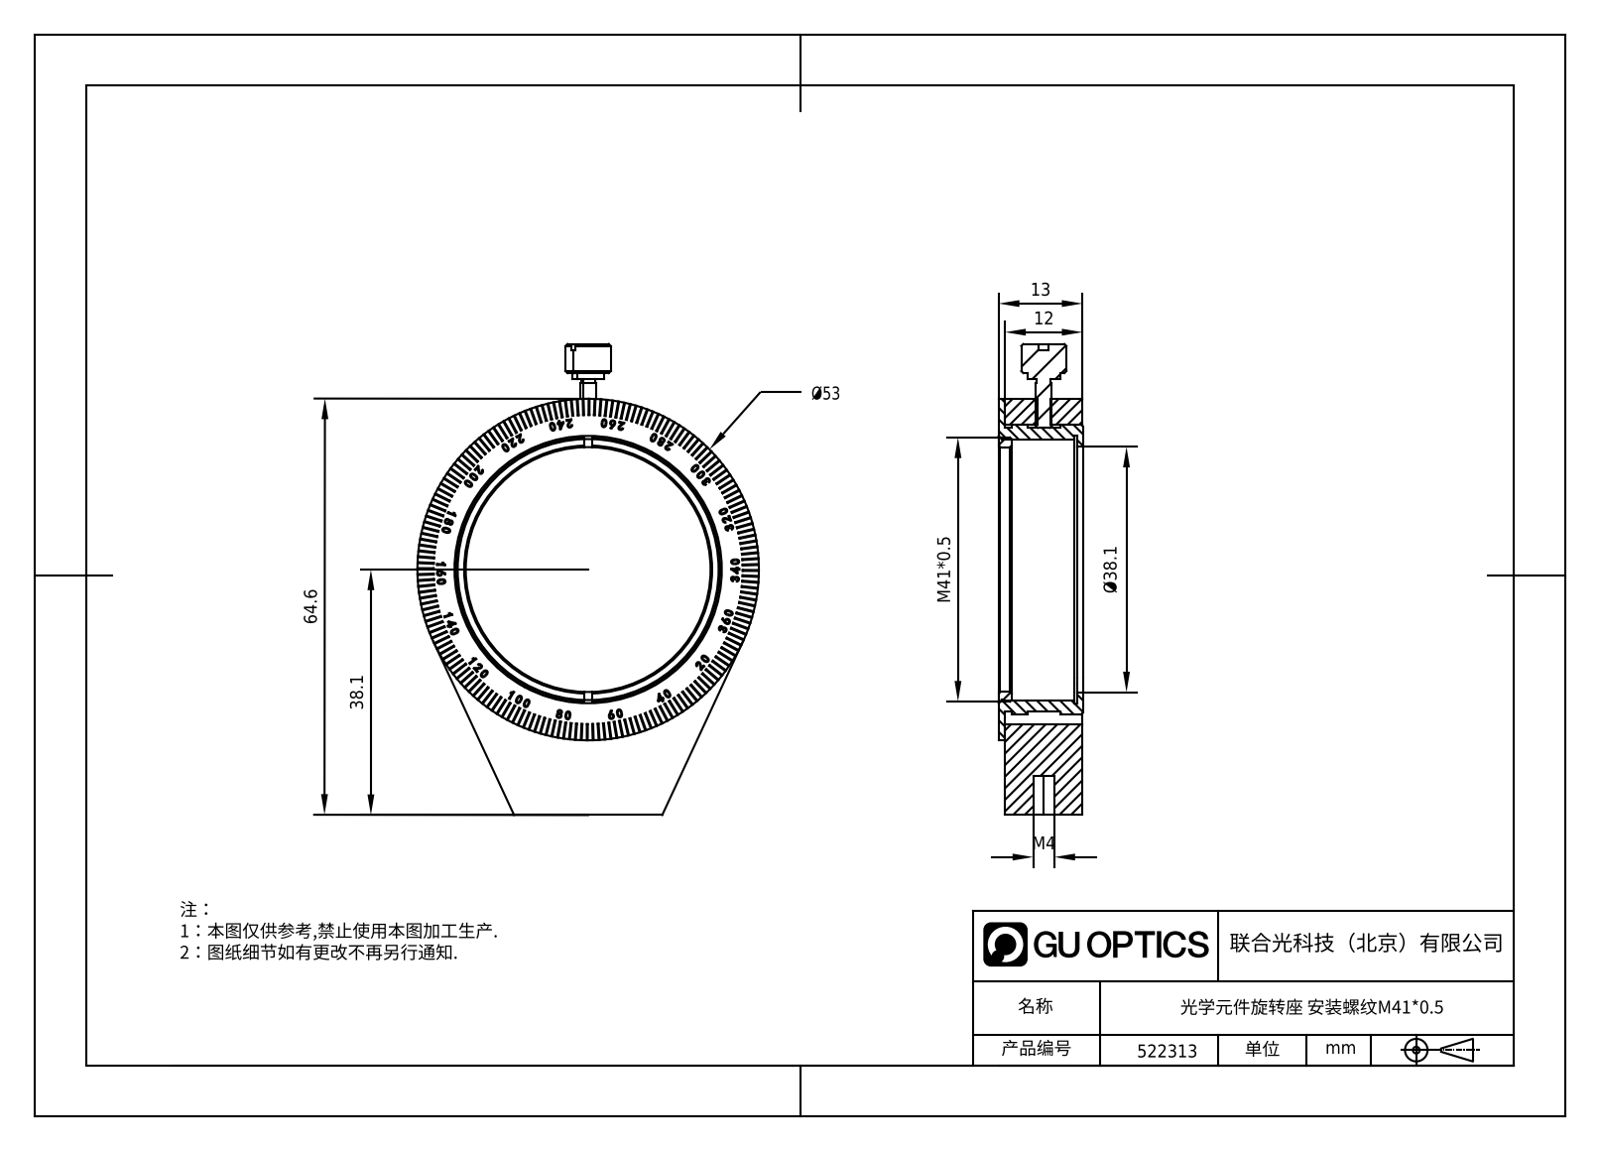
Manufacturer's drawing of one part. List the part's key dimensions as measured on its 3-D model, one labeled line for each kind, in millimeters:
Part name (STEP PRODUCT): ZFK透镜卡环压圈_1.8.5.55_ZFK-K40; 一体式手拧螺丝_30.13.2.2.5-SNTY-M2.5x7.5-0713
STEP written by: SolidWorks 2021 (CONFIG_CONTROL_DESIGN)
Units: millimetres
Bodies: 4 solids, 1216 faces (987 planar, 37 cylindrical, 192 other)
Overall size (bounding box): 73.1 × 53 × 13.05
Volume: 16 835 mm³ · Surface area: 13 243 mm²
Round holes (diameter × count): ⌀2.05 ×1, ⌀3.3 ×1, ⌀38 ×1, ⌀38.1 ×1, ⌀40.5 ×1, ⌀41.5 ×1
Round bosses / shafts (diameter × count): ⌀53 ×1, ⌀45 ×1, ⌀44 ×1, ⌀41 ×1, ⌀7 ×1, ⌀5 ×1, ⌀2.5 ×1, ⌀2.1 ×1
Partial cylindrical surfaces — rounded edges, fillets, slot ends (radius × count): R19 ×1
Main face-to-face distances: 1, 12, 13, 12.05, 13.05, 0.8, 0.75, 11.25, 12.25, 11
